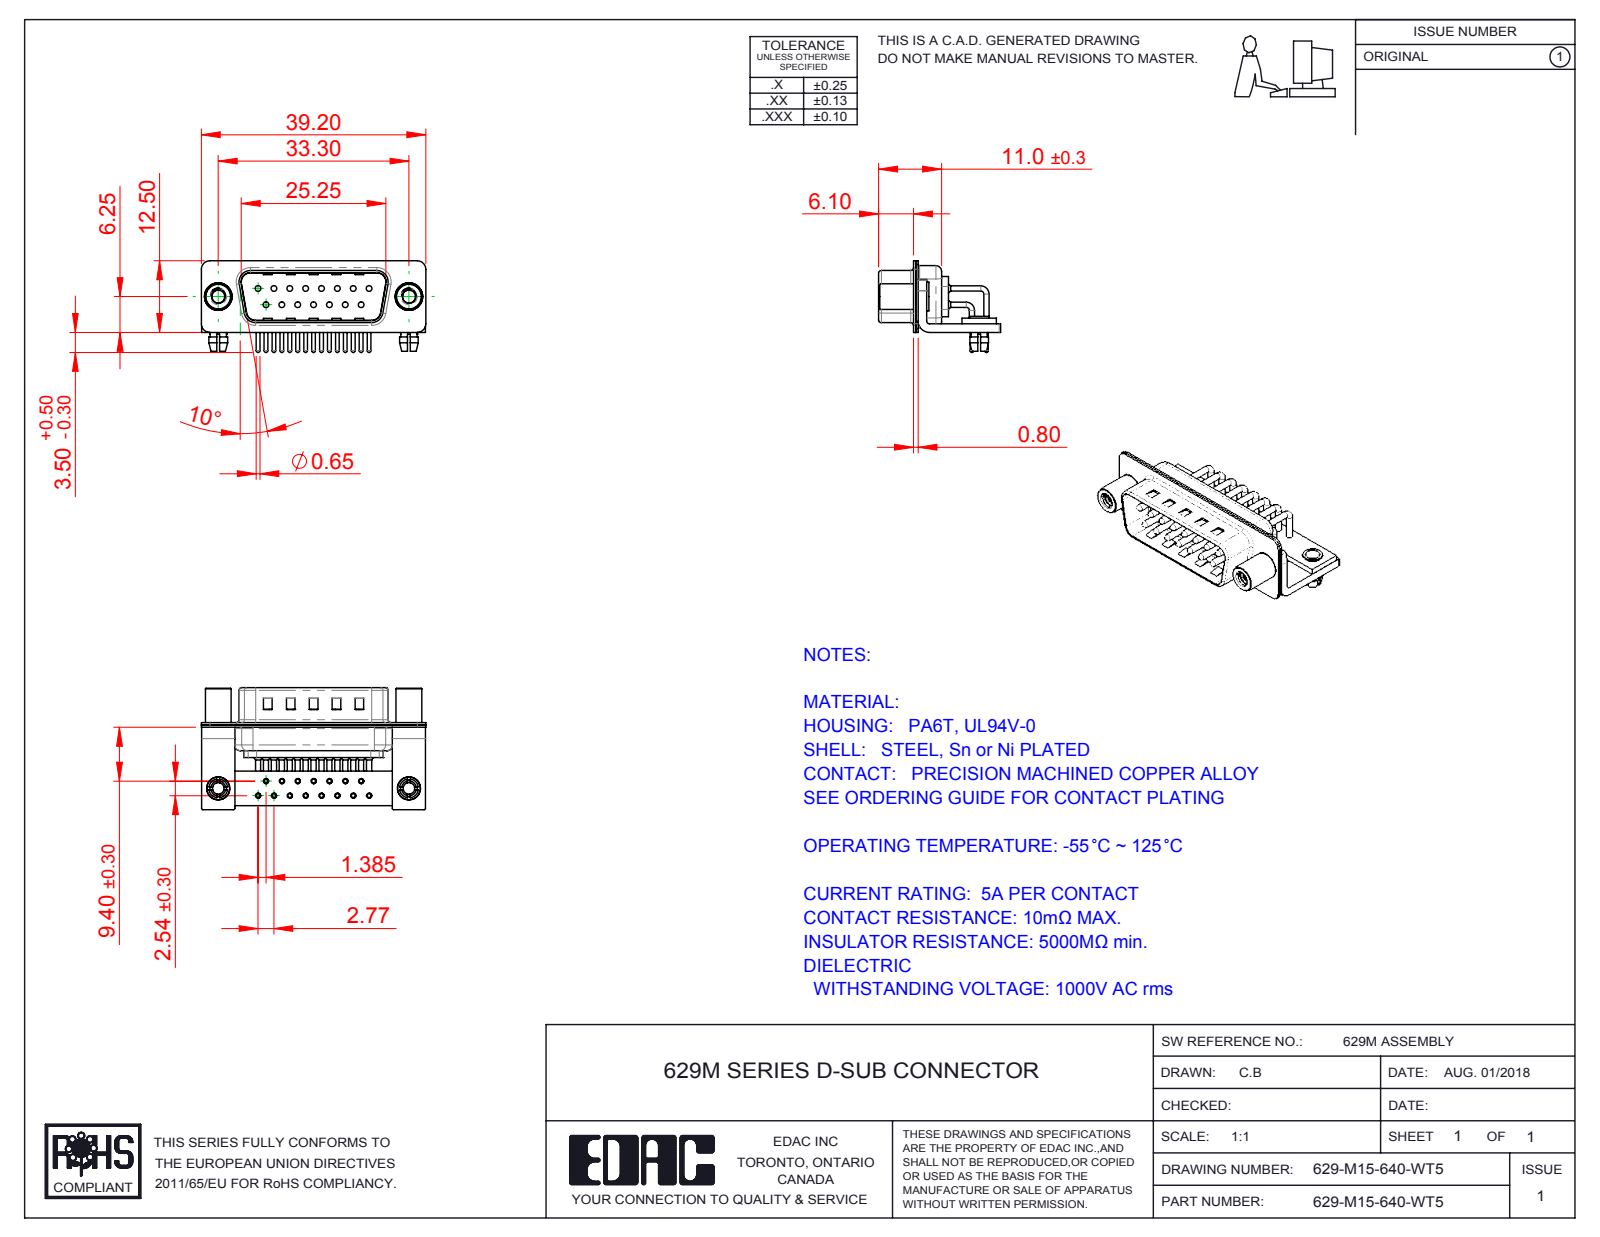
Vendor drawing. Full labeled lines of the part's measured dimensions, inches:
Part name (STEP PRODUCT): 629M Contact Row 2; 629M 4-40 Threaded Standoff; 629-M15-640-WT5; 629M Stabilizer Board_15 Contacts (+6 more)
STEP written by: SolidWorks 2016 (CONFIG_CONTROL_DESIGN)
Units: inches
Bodies: 25 solids, 2212 faces (1175 planar, 799 cylindrical, 238 other)
Overall size (bounding box): 1.543 × 0.839 × 0.63
Volume: 0.159 in³ · Surface area: 10.99 in²
Round holes (diameter × count): ⌀0.079 ×17, ⌀0.035 ×15, ⌀0.039 ×15, ⌀0.067 ×15, ⌀0.089 ×2, ⌀0.098 ×2, ⌀0.126 ×2, ⌀0.157 ×2, ⌀0.189 ×2
Round bosses / shafts (diameter × count): ⌀0.035 ×21, ⌀0.059 ×15, ⌀0.026 ×15, ⌀0.197 ×2, ⌀0.193 ×2, ⌀0.177 ×2, ⌀0.157 ×2, ⌀0.134 ×2
Partial cylindrical surfaces — rounded edges, fillets, slot ends (radius × count): R0.01 ×16, R0.059 ×16, R0.04 ×15, R0.079 ×13, R0.02 ×9, R0.063 ×8, R0.024 ×4, R0.026 ×4
Main face-to-face distances: 0.016, 0.059, 0.033, 0.031, 0.049, 0.409, 0.376, 0.039, 0.075, 0.327
Hole centre spacings: 0.109, 0.218, 0.124, 0.327, 0.192, 0.436, 0.114, 0.29
